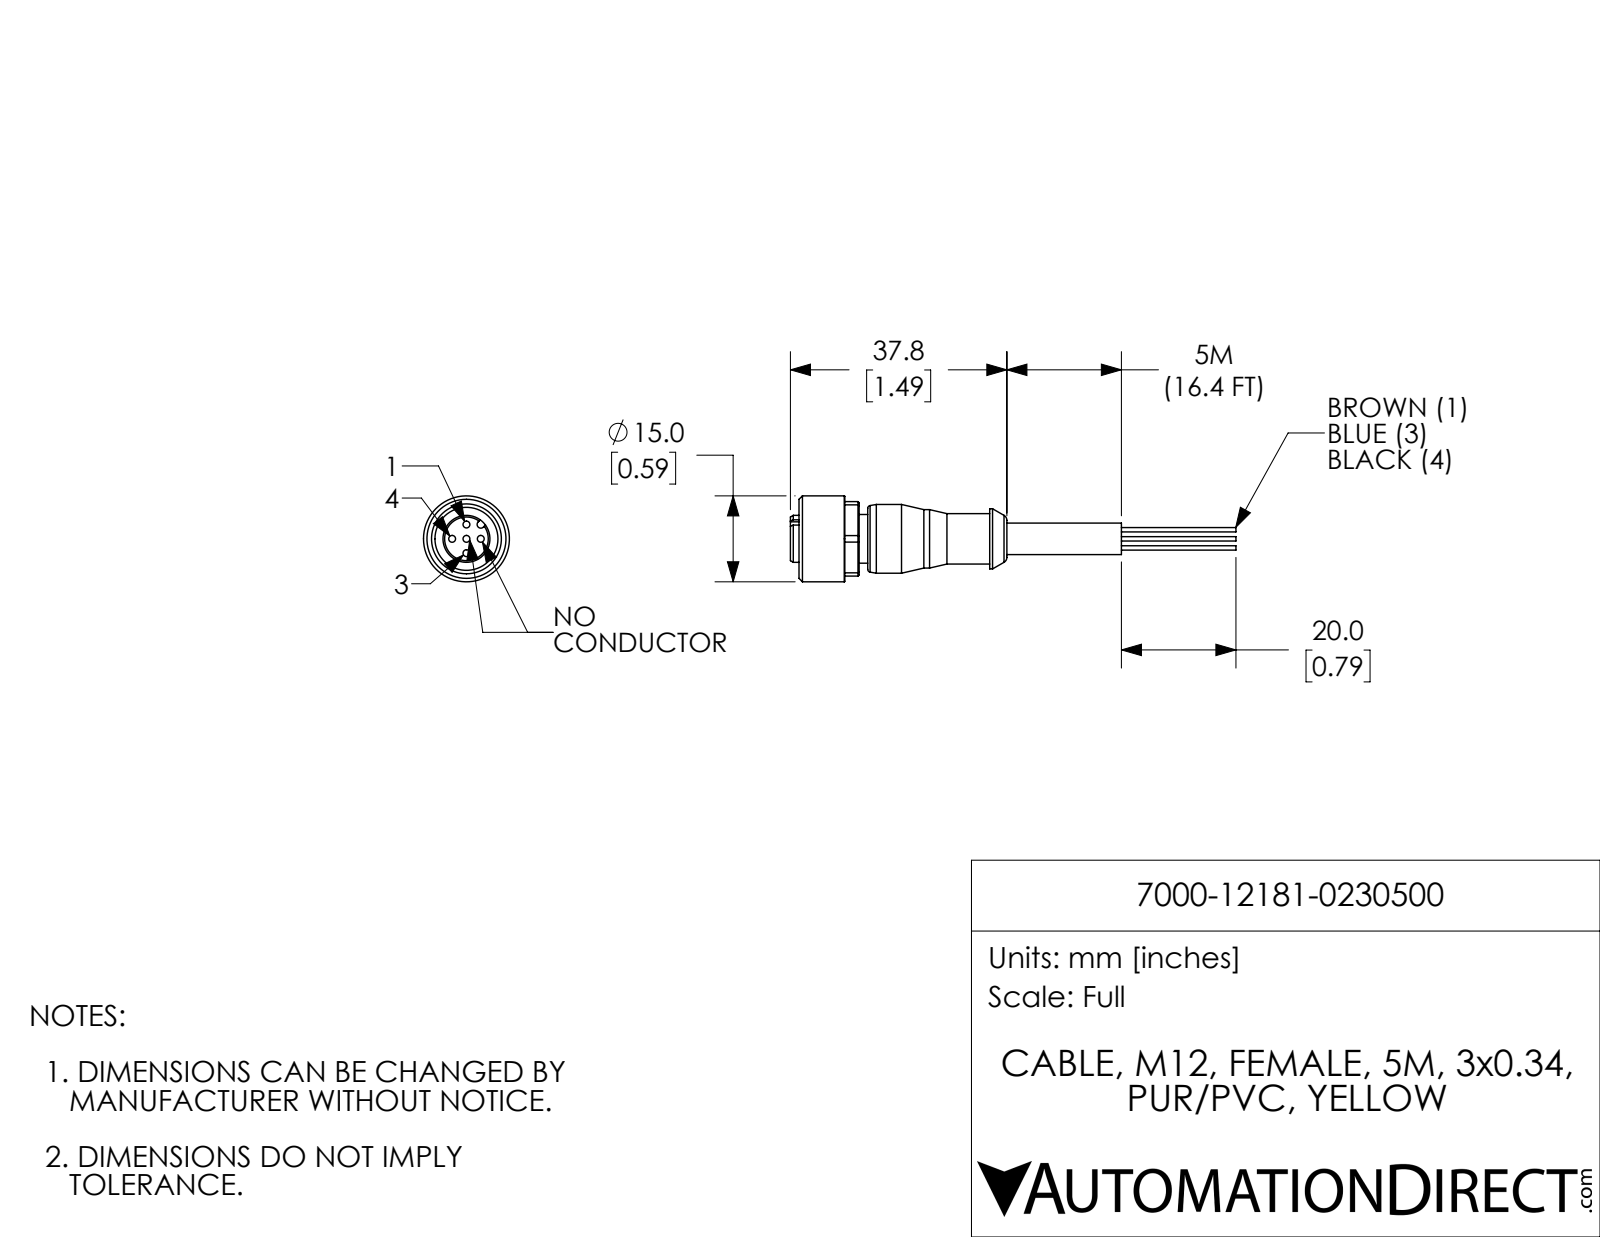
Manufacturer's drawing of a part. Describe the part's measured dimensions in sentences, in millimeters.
The part is named "7000-12181-0230500". Its 3-D file was written by "SolidWorks 2017 (AUTOMOTIVE_DESIGN)". It is 1 solid with 100 faces: 32 planar, 41 cylindrical and 27 other. Overall it measures 77.8 by 15 by 15 millimeters. Its volume is 4 050 cubic millimeters and its surface area 2 810 square millimeters. Round holes: 5 of diameter 1.2, 1 of diameter 11. Round bosses or shafts: 3 of diameter 0.8, 1 of diameter 15, 1 of diameter 12, 1 of diameter 10.5, 1 of diameter 10.2, 1 of diameter 8.8, 1 of diameter 8.5, 1 of diameter 8.2. Partial cylindrical surfaces (rounded edges, fillets, slot ends): 1 of radius 0.7, 1 of radius 7.2. The main face-to-face distances are 12, 1.5, 3, 13, 9, 25.8, 7.5, 10.5, 2.5, 13.5. The hole center spacings are 2.5, 3.5, 5.
